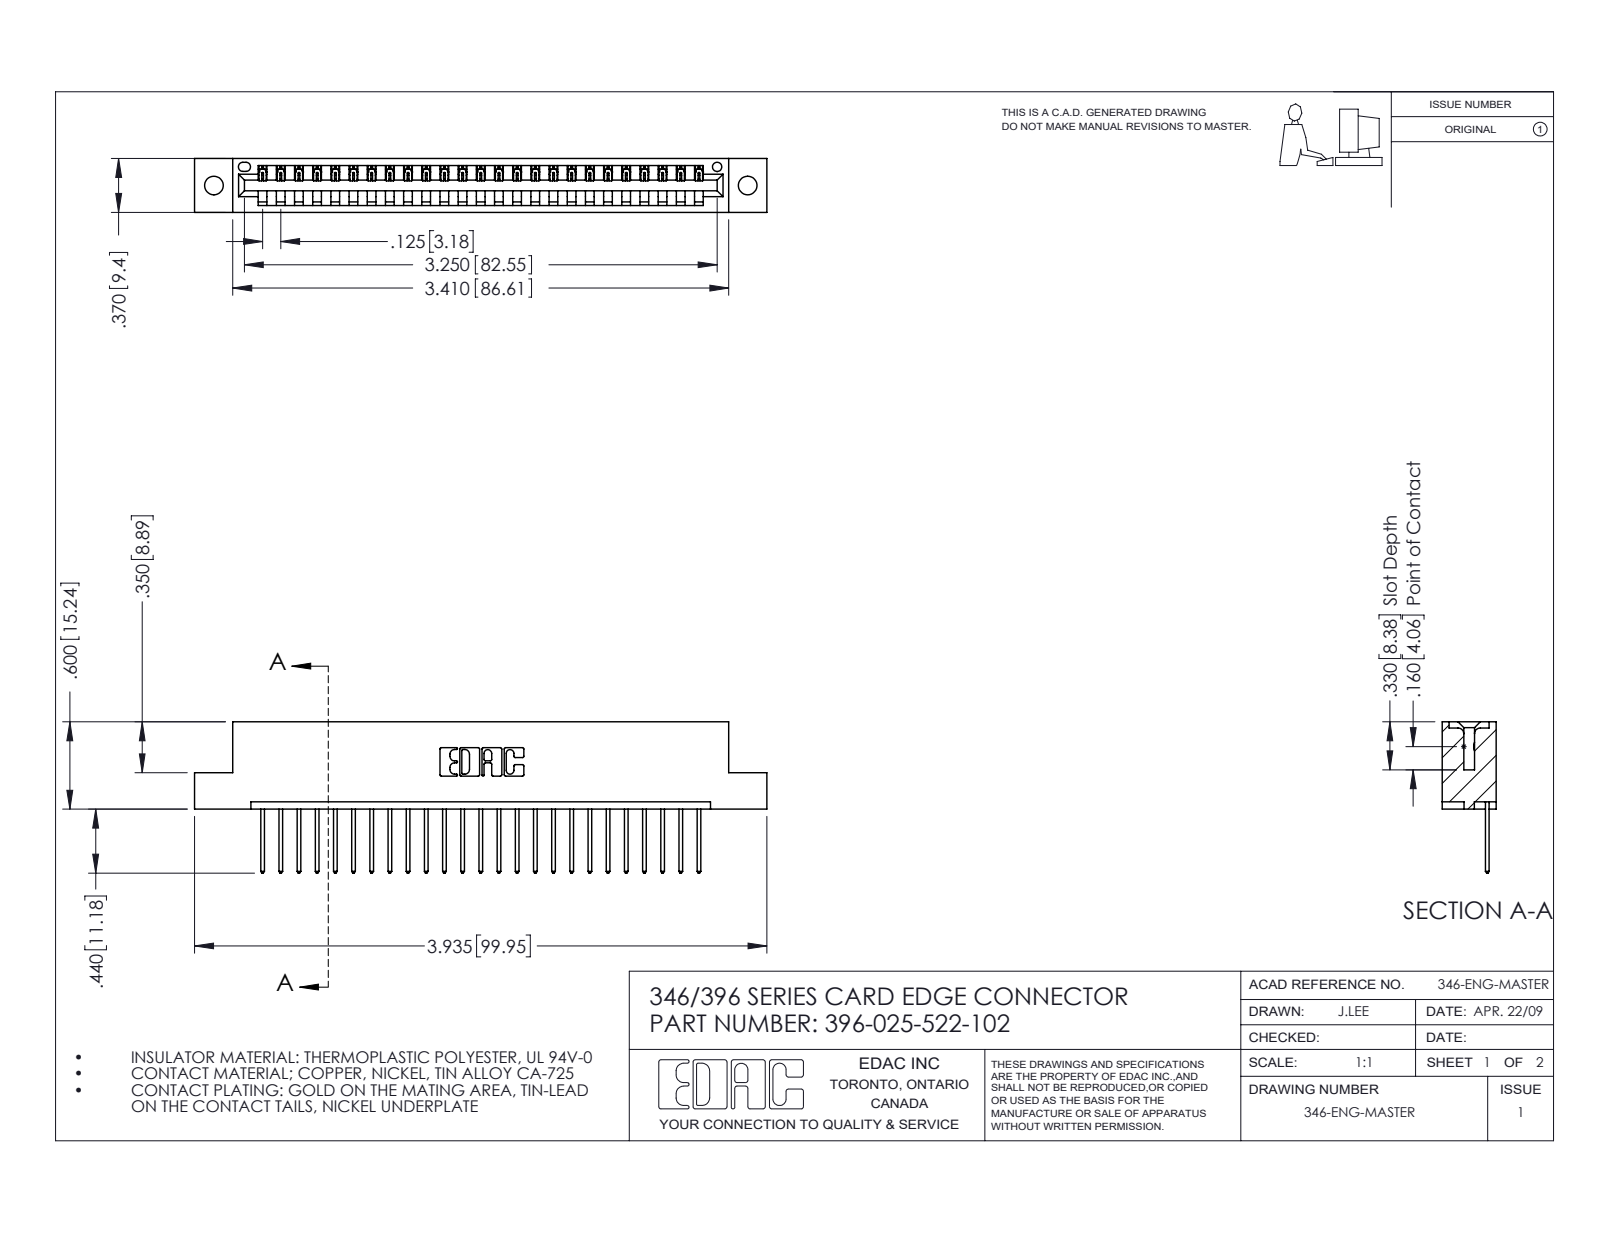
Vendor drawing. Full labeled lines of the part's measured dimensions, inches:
Part name (STEP PRODUCT): 345-292-001_345-293-122; 396-025-522-102; 346 Part_Flush Mounting Lugs - 0.128 Dia
STEP written by: SolidWorks 2016 (CONFIG_CONTROL_DESIGN)
Units: inches
Bodies: 26 solids, 1572 faces (1076 planar, 496 cylindrical, 0 other)
Overall size (bounding box): 3.935 × 1.04 × 0.37
Volume: 0.575 in³ · Surface area: 17.68 in²
Round holes (diameter × count): ⌀0.128 ×2, ⌀0.064 ×1
Partial cylindrical surfaces — rounded edges, fillets, slot ends (radius × count): R0.006 ×50, R0.01 ×50, R0.01 ×22, R0.007 ×6, R0.031 ×6, R0.026 ×3, R0.031 ×2, R0.04 ×2
Main face-to-face distances: 0.048, 0.322, 0.25, 0.37, 0.072, 0.298, 0.025, 0.148, 0.222, 0.1
Hole centre spacings: 0.246, 3.462, 3.67
